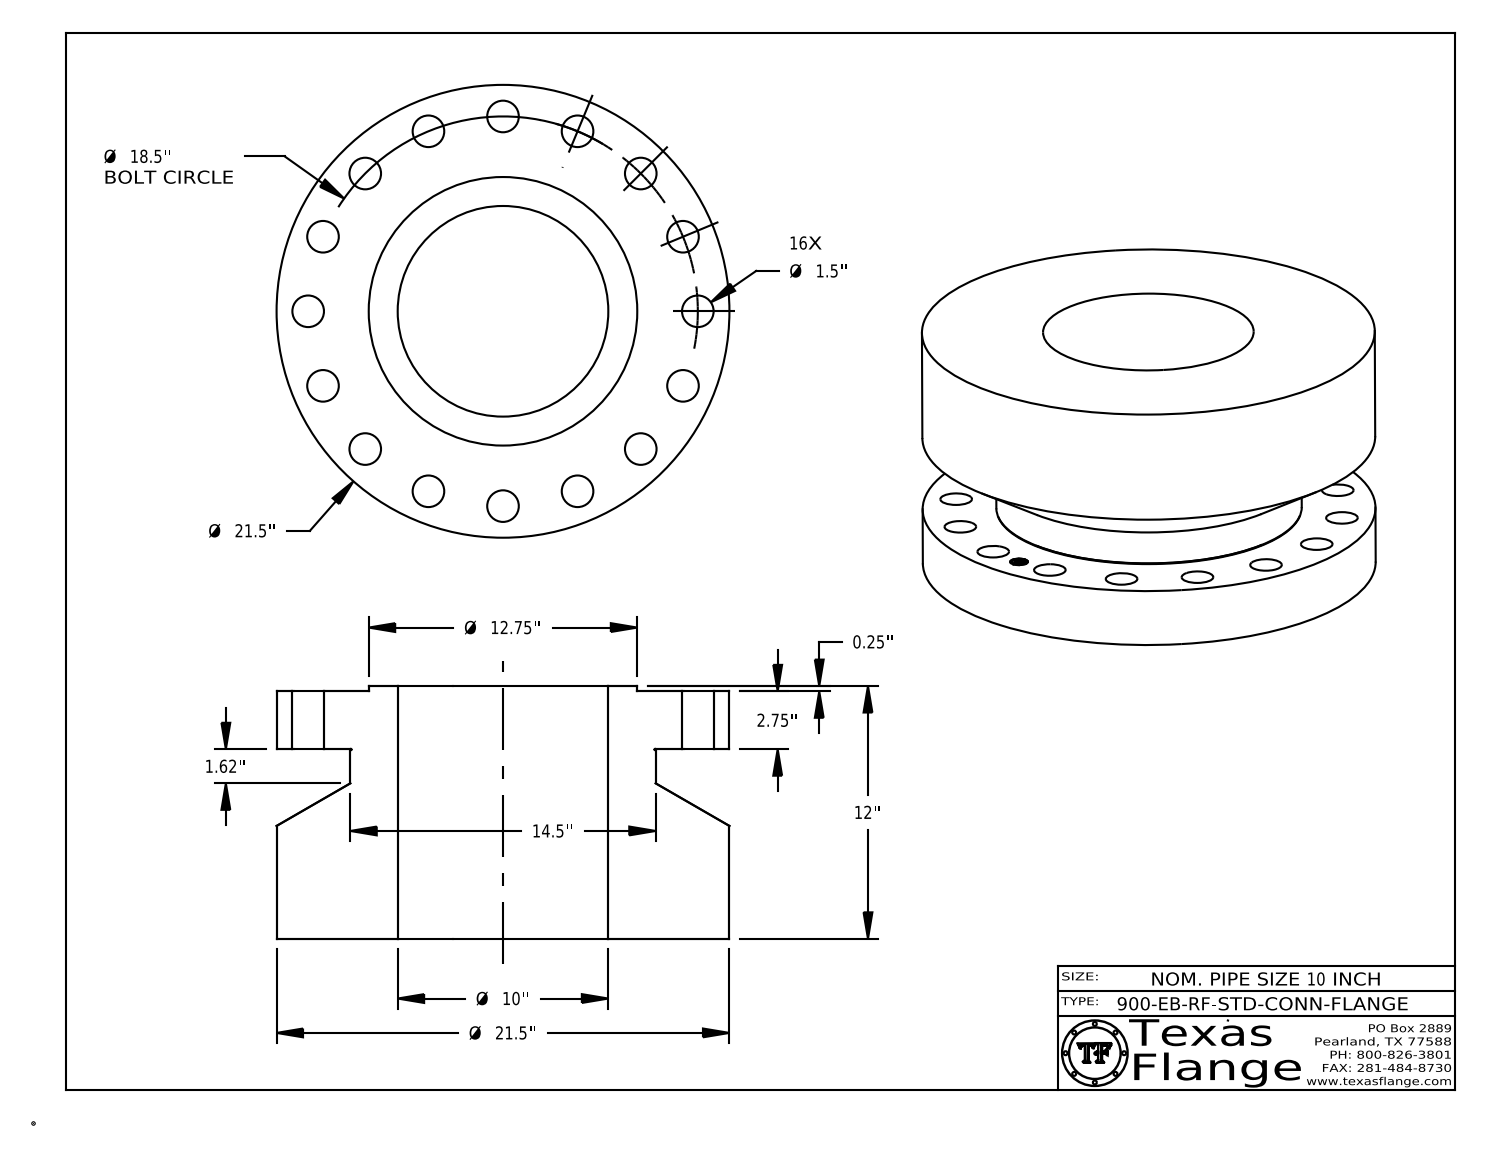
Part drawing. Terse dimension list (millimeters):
name: 10-900-EB-RF-STD-CONN-FLANGE
written by: CATIA V5 STEP AP214 (AUTOMOTIVE_DESIGN)
unit: mm
bodies: 1 solid, 437 faces (369 planar, 62 cylindrical, 6 other)
size: 546.1 × 546.1 × 304.8
volume: 44 970 000 mm³; area: 1 392 000 mm²
holes: 16× ⌀38.1, 1× ⌀21.6, 1× ⌀254
bosses: 8× ⌀1.3, 1× ⌀546.1, 1× ⌀368.3, 1× ⌀323.9, 1× ⌀17
face distances: 298.5, 69.9, 228.6, 6.4, 76.2, 304.8, 76.1, 69.7, 228.7, 0.4
hole spacings: 390.7, 179.8, 235, 332.3, 91.7, 91.7, 261.1, 261.1
